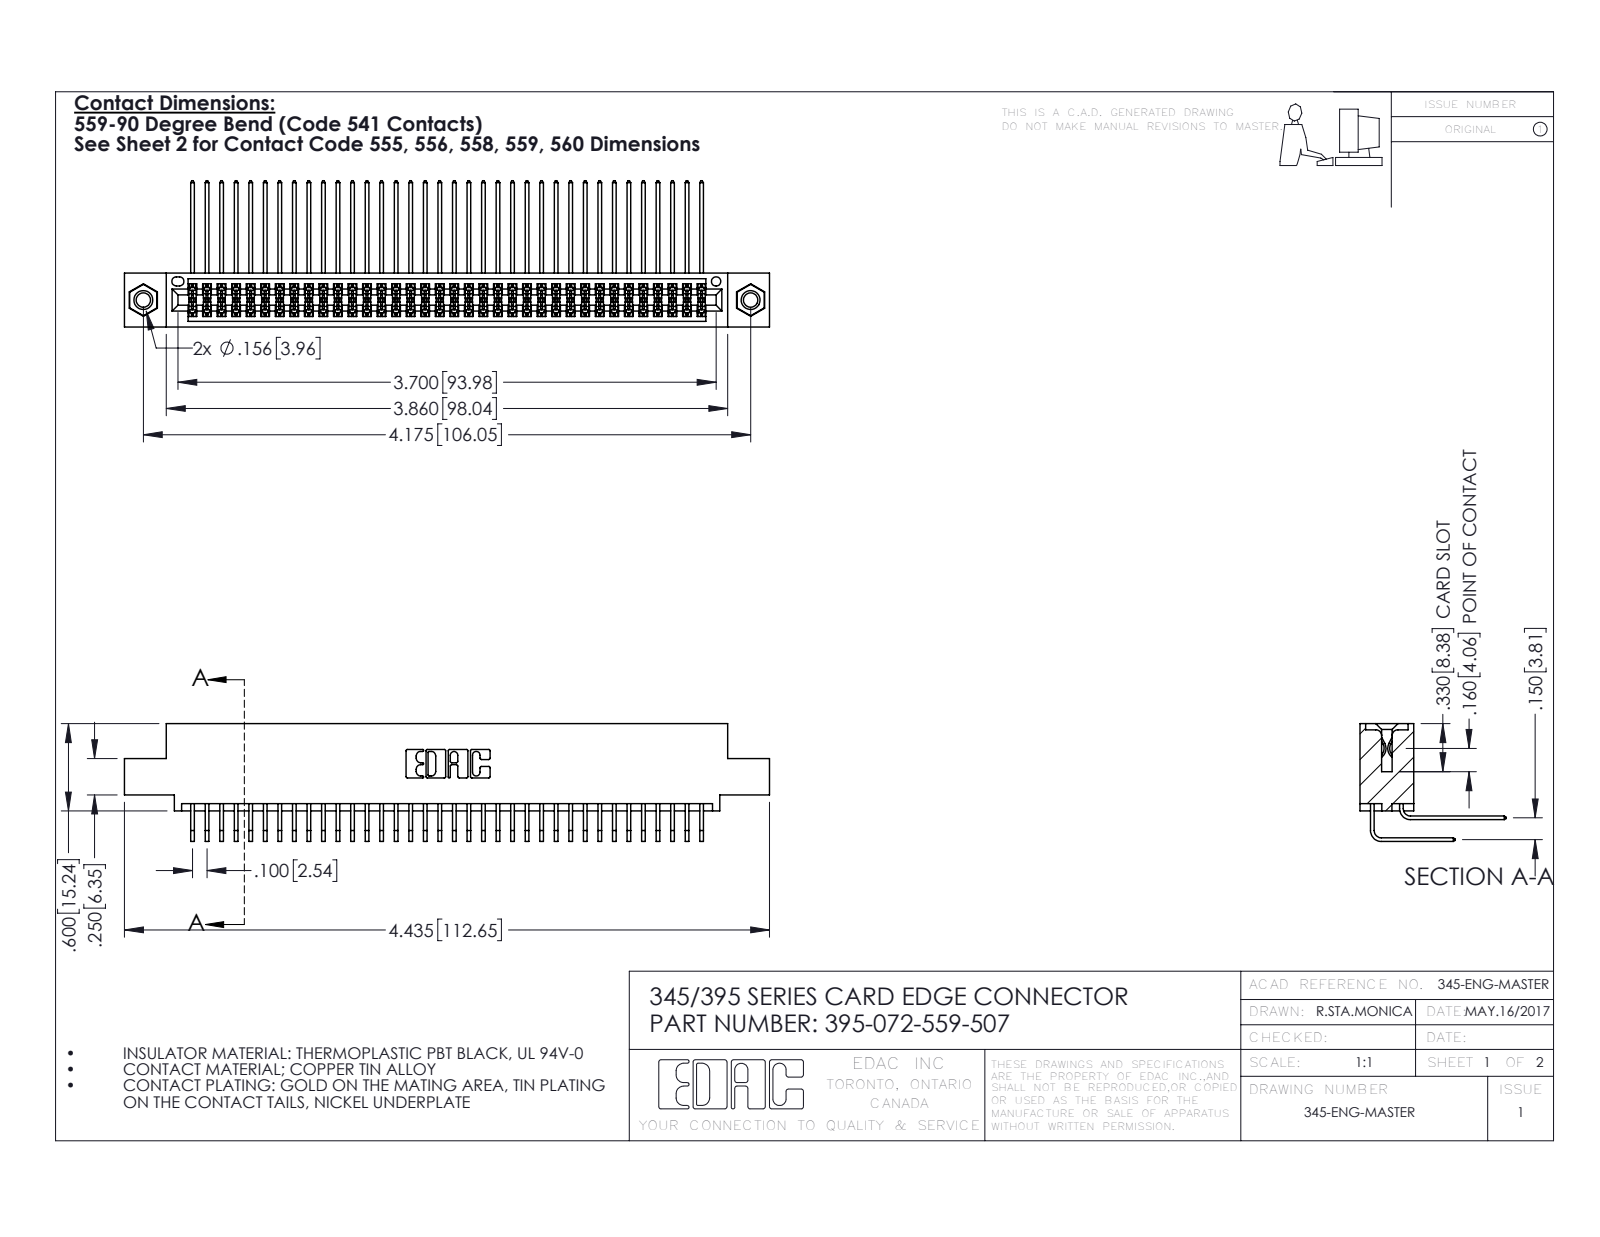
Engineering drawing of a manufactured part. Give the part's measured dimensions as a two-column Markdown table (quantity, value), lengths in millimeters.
| quantity | value |
| --- | --- |
| part name | 345-292-001_558 559 Tail - 1; 345-250-001_345-250-005-103; 345-292-001_559 Tail - 2; 395-072-559-507 (+1 more) |
| STEP written by | SolidWorks 2016 (CONFIG_CONTROL_DESIGN) |
| units | millimeters |
| bodies | 75 solids, 3934 faces (2636 planar, 1282 cylindrical, 16 other) |
| overall size | 112.6 × 25.5 × 20.5 |
| volume | 11 200 mm³ |
| surface area | 18 540 mm² |
| round holes (diameter × count) | 2.5 × 2, 3.2 × 2, 4 × 2, 1.6 × 1 |
| round bosses / shafts (diameter × count) | 3.9 × 2 |
| partial cylindrical surfaces (radius × count) | 0.2 × 108, 0.3 × 22, 0.2 × 6, 0.8 × 6, 0.7 × 3, 0.4 × 2, 0.5 × 2, 0.6 × 2 |
| main face-to-face distances | 1.8, 7.6, 5.1, 9.4, 2.5, 6.9, 0.6, 5.7, 4.4, 3.8 |
| hole center spacings | 6.9, 100.1, 106 |
